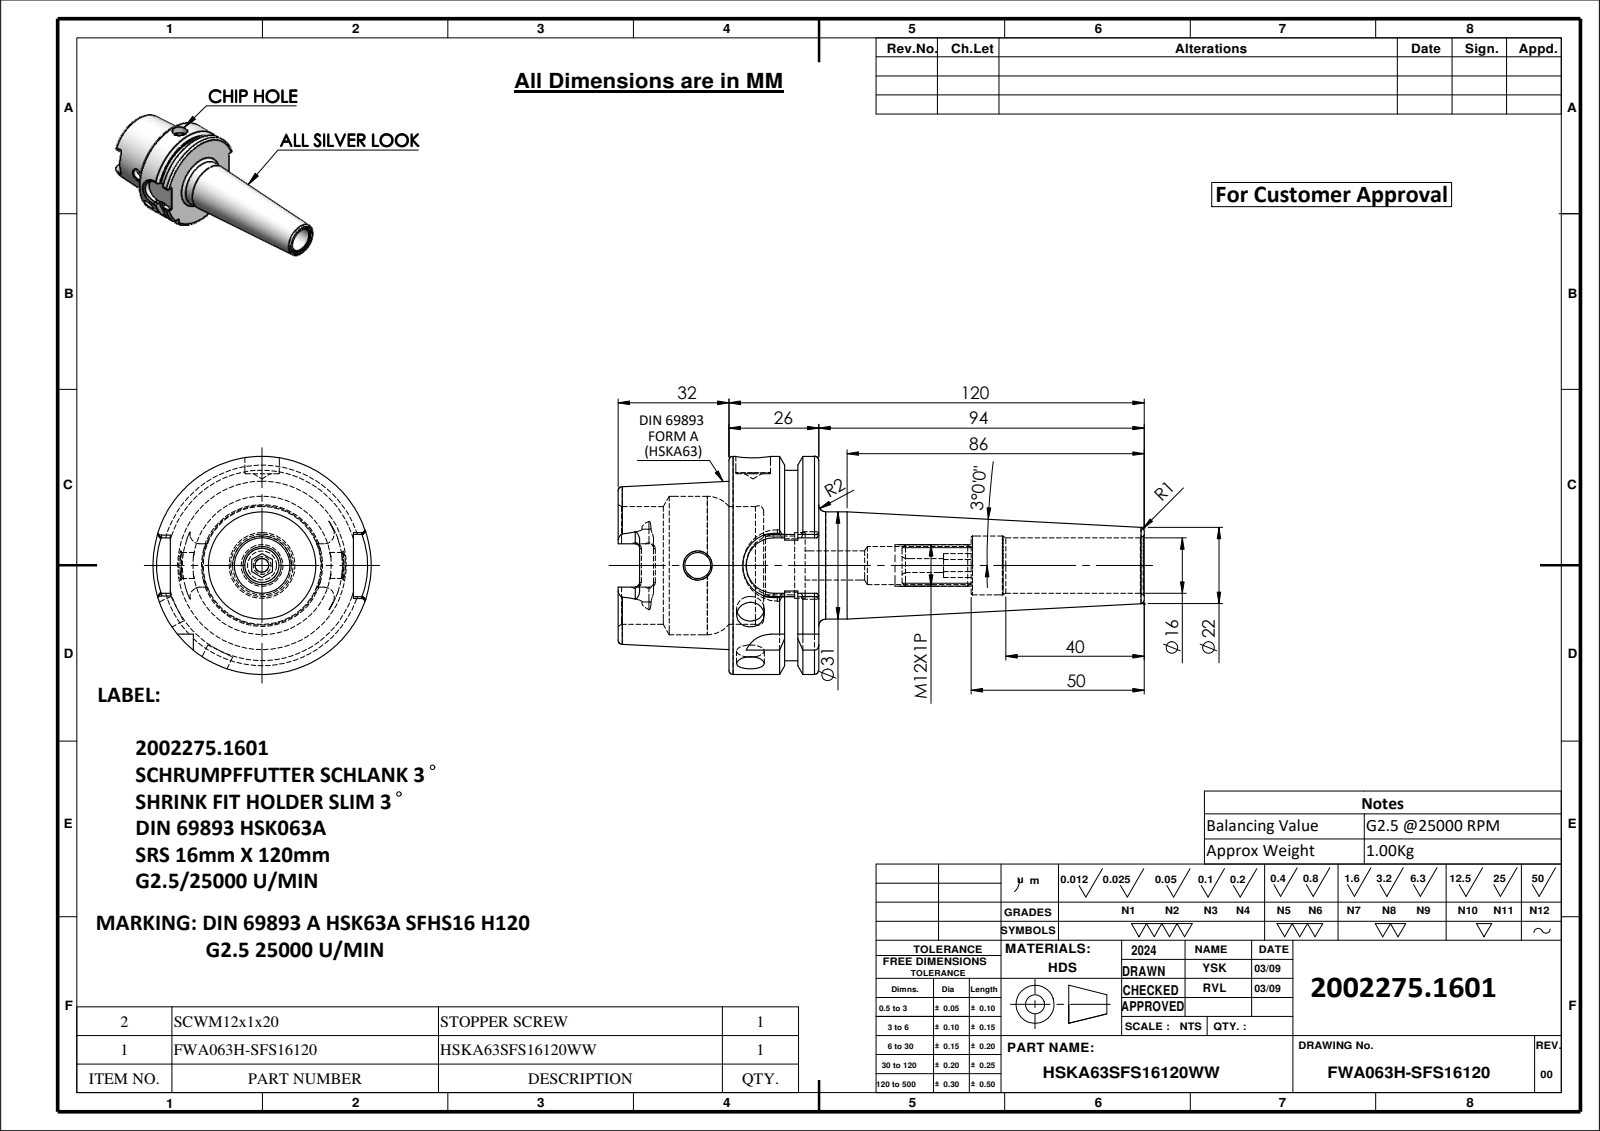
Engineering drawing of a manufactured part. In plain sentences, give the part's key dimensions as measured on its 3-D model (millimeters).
The part is named "SCWM12X1P; HSKA63SFS16120WW; FWA063H-SFS16120". Its 3-D file was written by "SolidWorks 2024 (CONFIG_CONTROL_DESIGN)". It is 2 solids with 196 faces: 59 planar, 57 cylindrical and 80 other. Overall it measures 152 by 63 by 63 millimeters. Its volume is 122 735 cubic millimeters and its surface area 34 967 square millimeters. Round holes: 2 of diameter 8, 1 of diameter 4, 1 of diameter 7.5, 1 of diameter 8.4, 1 of diameter 10, 1 of diameter 11, 1 of diameter 16, 1 of diameter 17, 1 of diameter 19, 1 of diameter 34, 1 of diameter 40. Round bosses or shafts: 1 of diameter 63, 1 of diameter 55, 1 of diameter 31, 1 of diameter 12. Partial cylindrical surfaces (rounded edges, fillets, slot ends): 6 of radius 1.3, 4 of radius 2.88, 2 of radius 8, 1 of radius 9. The main face-to-face distances are 25.95, 10, 15.95, 32, 42, 57.95, 52.9, 12, 54, 22.
